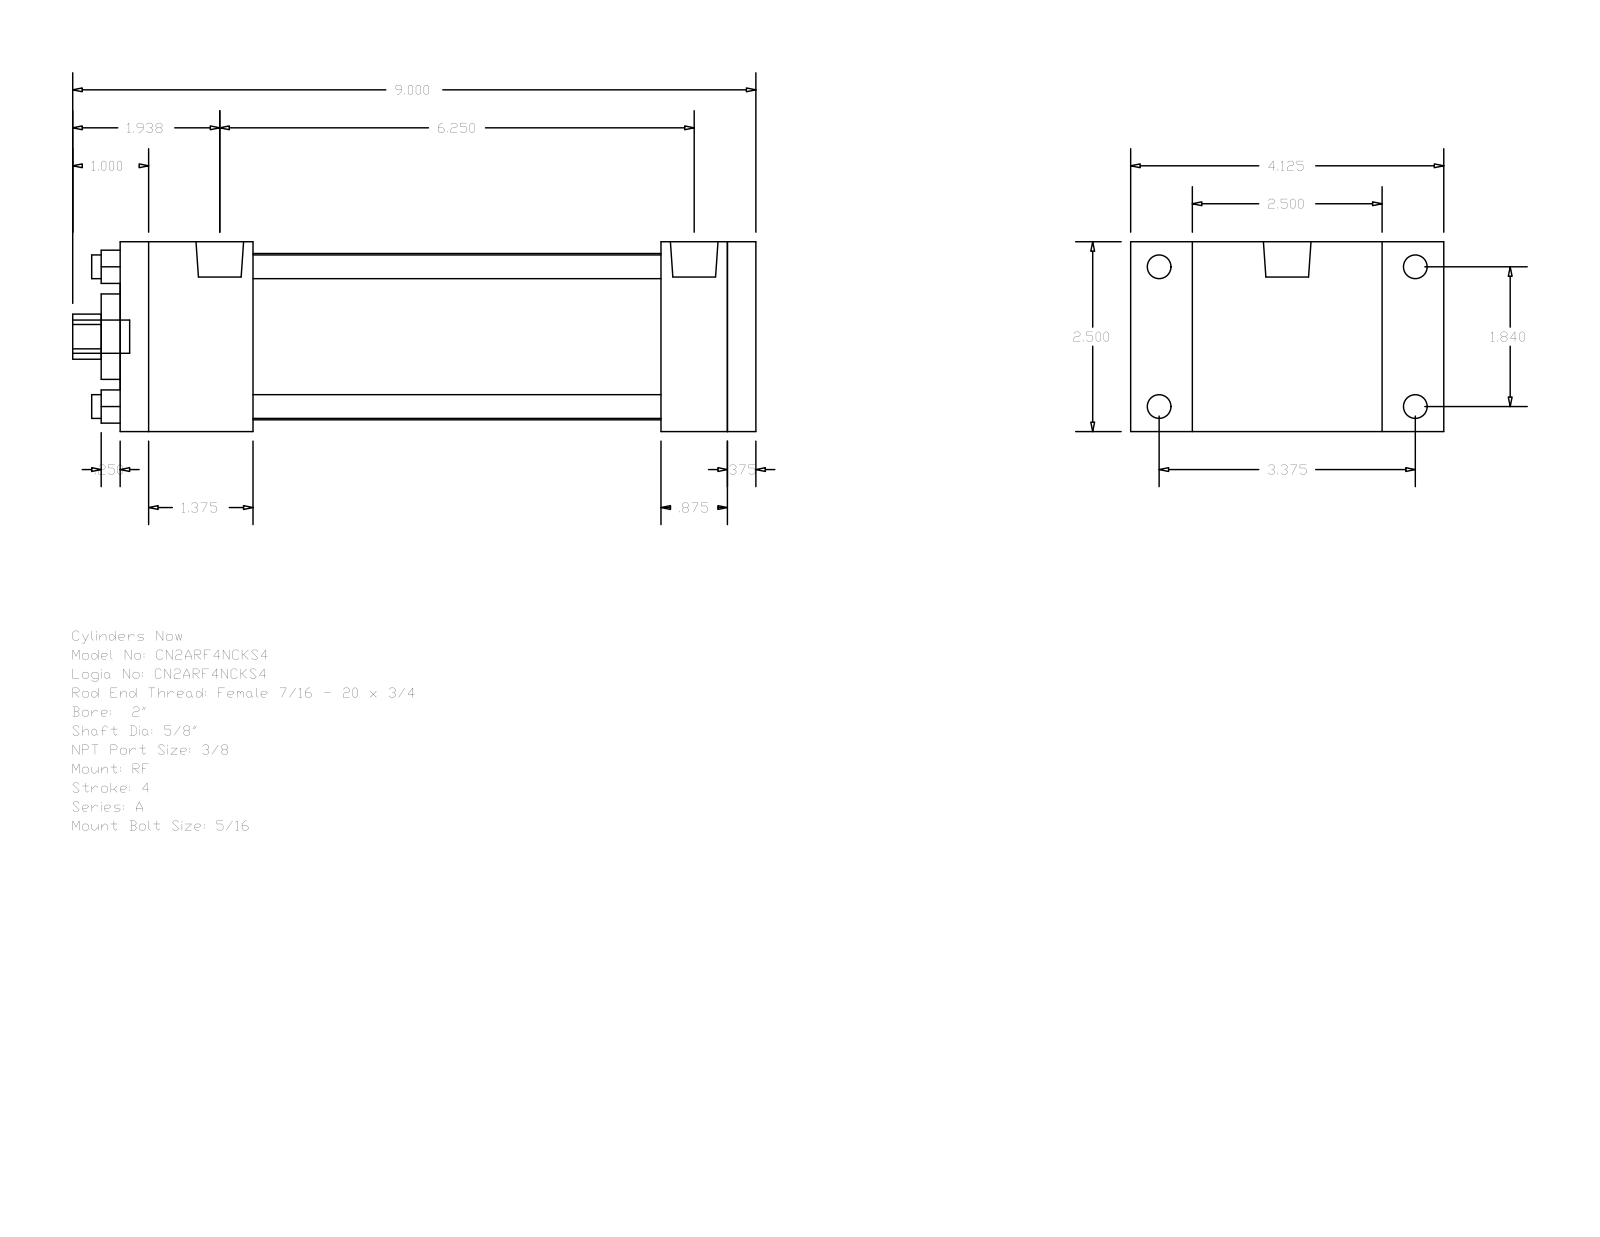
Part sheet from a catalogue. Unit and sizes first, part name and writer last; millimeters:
Units: millimetres
Overall size (bounding box): 228.6 × 104.78 × 63.5
Round holes (diameter × count): ⌀7.94 ×4, ⌀15.88 ×1, ⌀28.57 ×1, ⌀55.63 ×1
Round bosses / shafts (diameter × count): ⌀7.94 ×4, ⌀5.56 ×4, ⌀15.93 ×2, ⌀11.11 ×1
Partial cylindrical surfaces — rounded edges, fillets, slot ends (radius × count): R7.54 ×1
Main face-to-face distances: 63.5, 212.72, 9.53, 203.19, 44.45, 158.74, 168.27, 180.97, 136.52, 22.22
Hole centre spacings: 33.05, 46.74, 66.1
Bodies: 0 solids, 92 faces (64 planar, 28 cylindrical, 0 other)
Part name (STEP PRODUCT): A_RF__0200_0.625
STEP written by: GSSL Pune (CONFIG_CONTROL_DESIGN)
